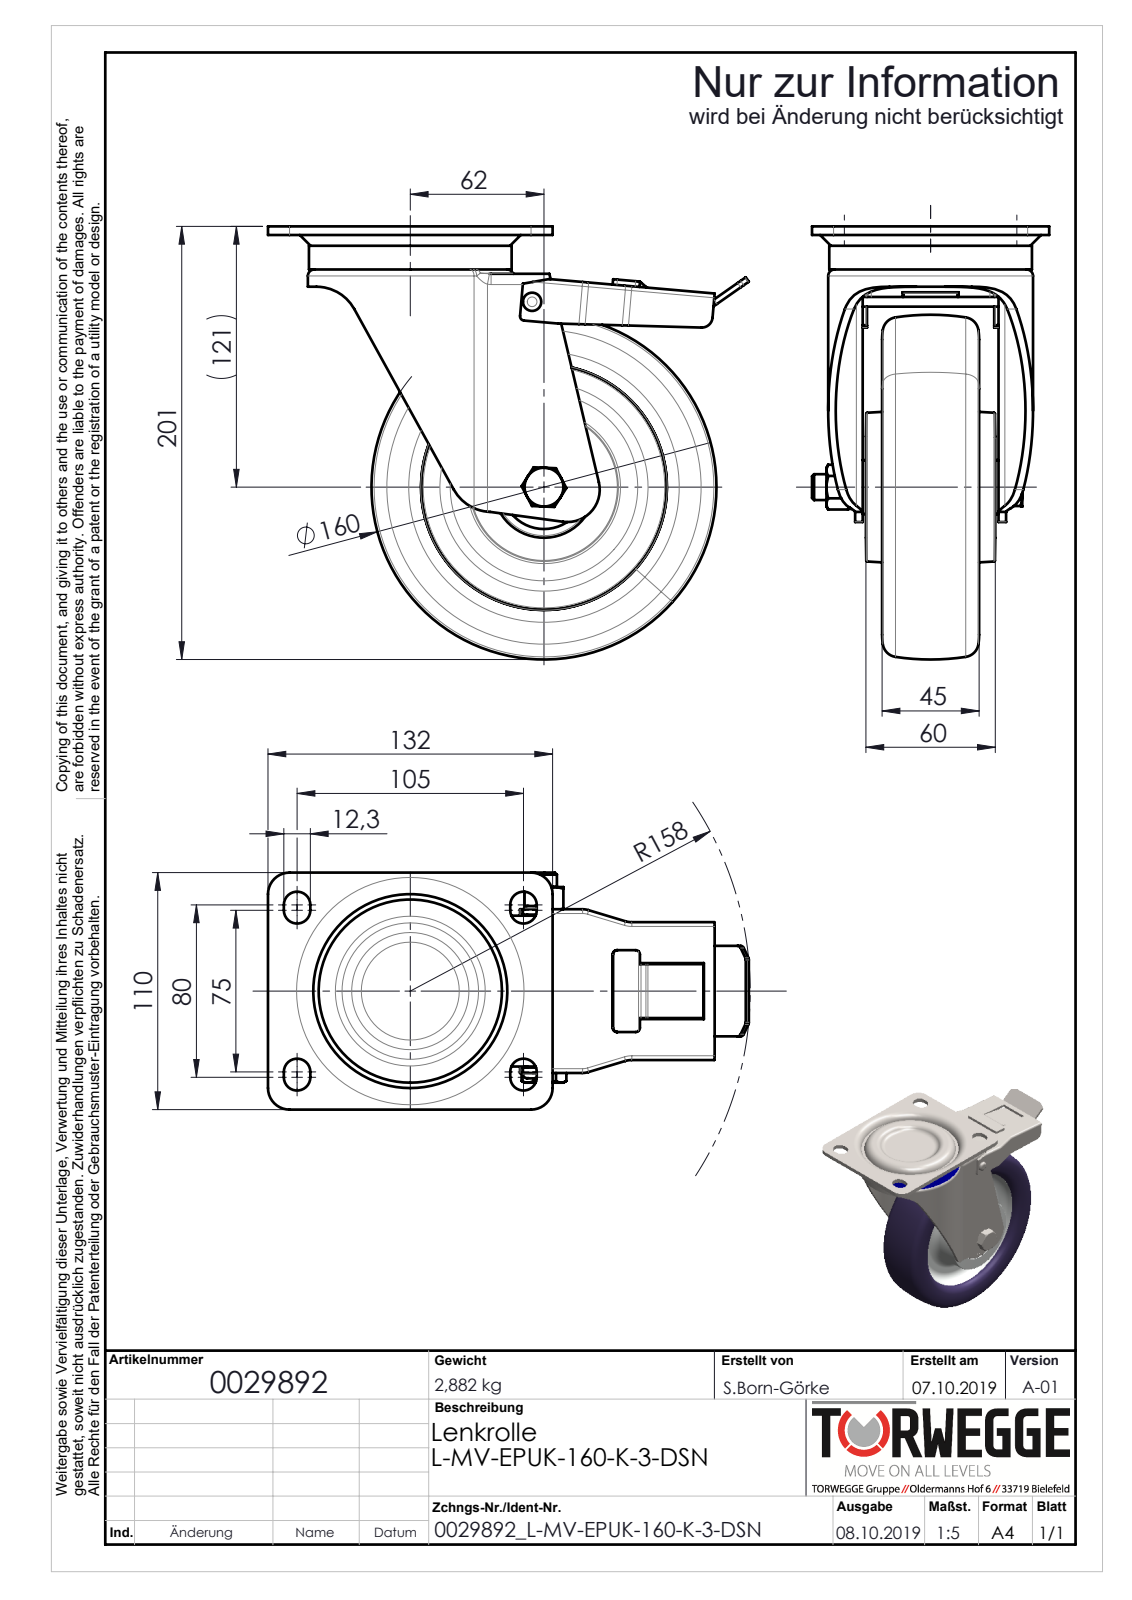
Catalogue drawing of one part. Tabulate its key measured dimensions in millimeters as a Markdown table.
| quantity | value |
| --- | --- |
| part name | 0029892_L-MV-EPUK-160-K-3-DSN_(A-01) |
| STEP written by | SolidWorks 2018 (AUTOMOTIVE_DESIGN) |
| units | millimeters |
| bodies | 13 solids, 608 faces (192 planar, 192 cylindrical, 224 other) |
| overall size | 223.02 × 201 × 110 |
| volume | 976 641 mm³ |
| surface area | 274 969 mm² |
| round holes (diameter × count) | 5 × 1, 10.2 × 1, 12 × 1, 12.2 × 1, 12.5 × 1, 20 × 1, 21 × 1, 35 × 1, 38.9 × 1 |
| round bosses / shafts (diameter × count) | 137 × 1, 94 × 1, 47 × 1, 28.1 × 1, 25 × 1, 20.2 × 1, 19.9 × 1, 18 × 1 |
| partial cylindrical surfaces (radius × count) | 2 × 26, 10 × 14, 6.15 × 8, 5 × 3, 1.5 × 2, 13.5 × 2, 20 × 2, 15 × 1 |
| main face-to-face distances | 3.5, 66.5, 20, 2.5, 23.5, 19.5, 2, 4, 46.5, 30 |
| hole center spacings | 86.18 |
